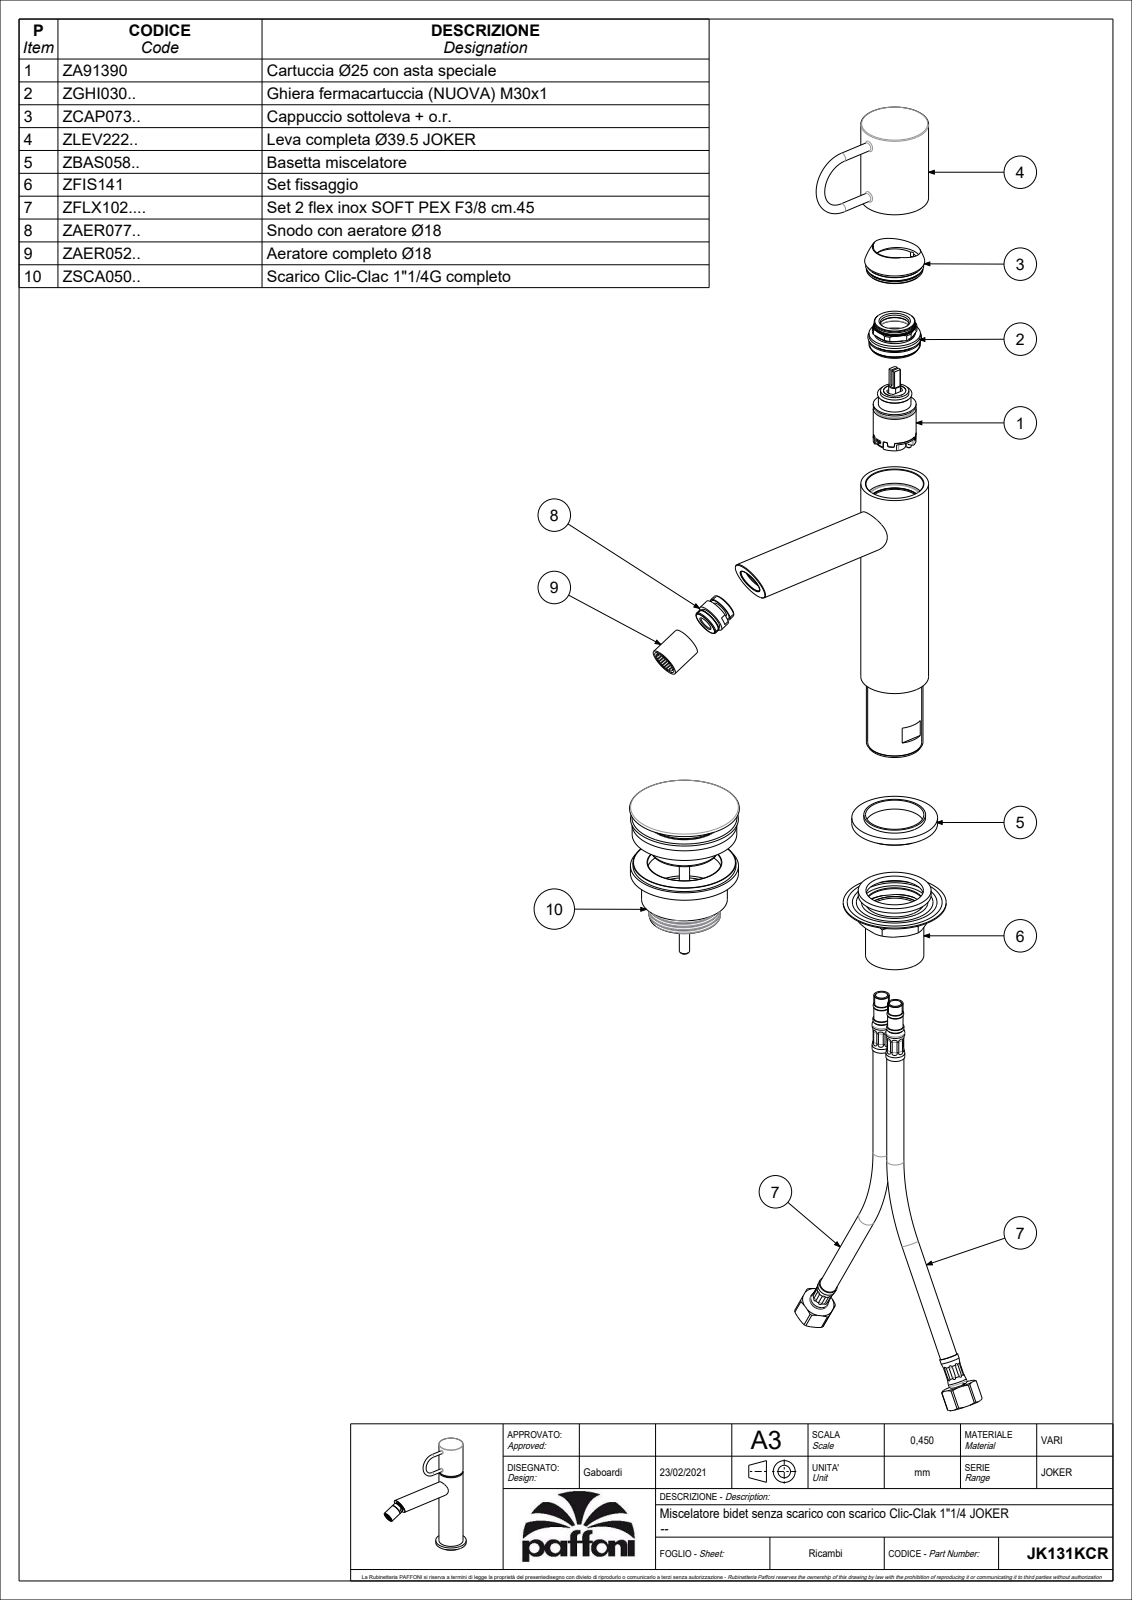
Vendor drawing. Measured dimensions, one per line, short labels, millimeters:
name: JK131CR
written by: CREO PARAMETRIC BY PTC INC, 2020044 (CONFIG_CONTROL_DESIGN)
unit: mm
bodies: 1 solid, 49 faces (13 planar, 20 cylindrical, 16 other)
size: 186.84 × 163.37 × 50
volume: 280 389 mm³; area: 38 149 mm²
bosses: 2× ⌀5, 1× ⌀50, 1× ⌀39.5, 1× ⌀24, 1× ⌀18, 1× ⌀14.5, 1× ⌀10
face distances: 4, 136.5, 132.5, 2.5, 134, 130, 27, 24.49, 2.51, 18.49
